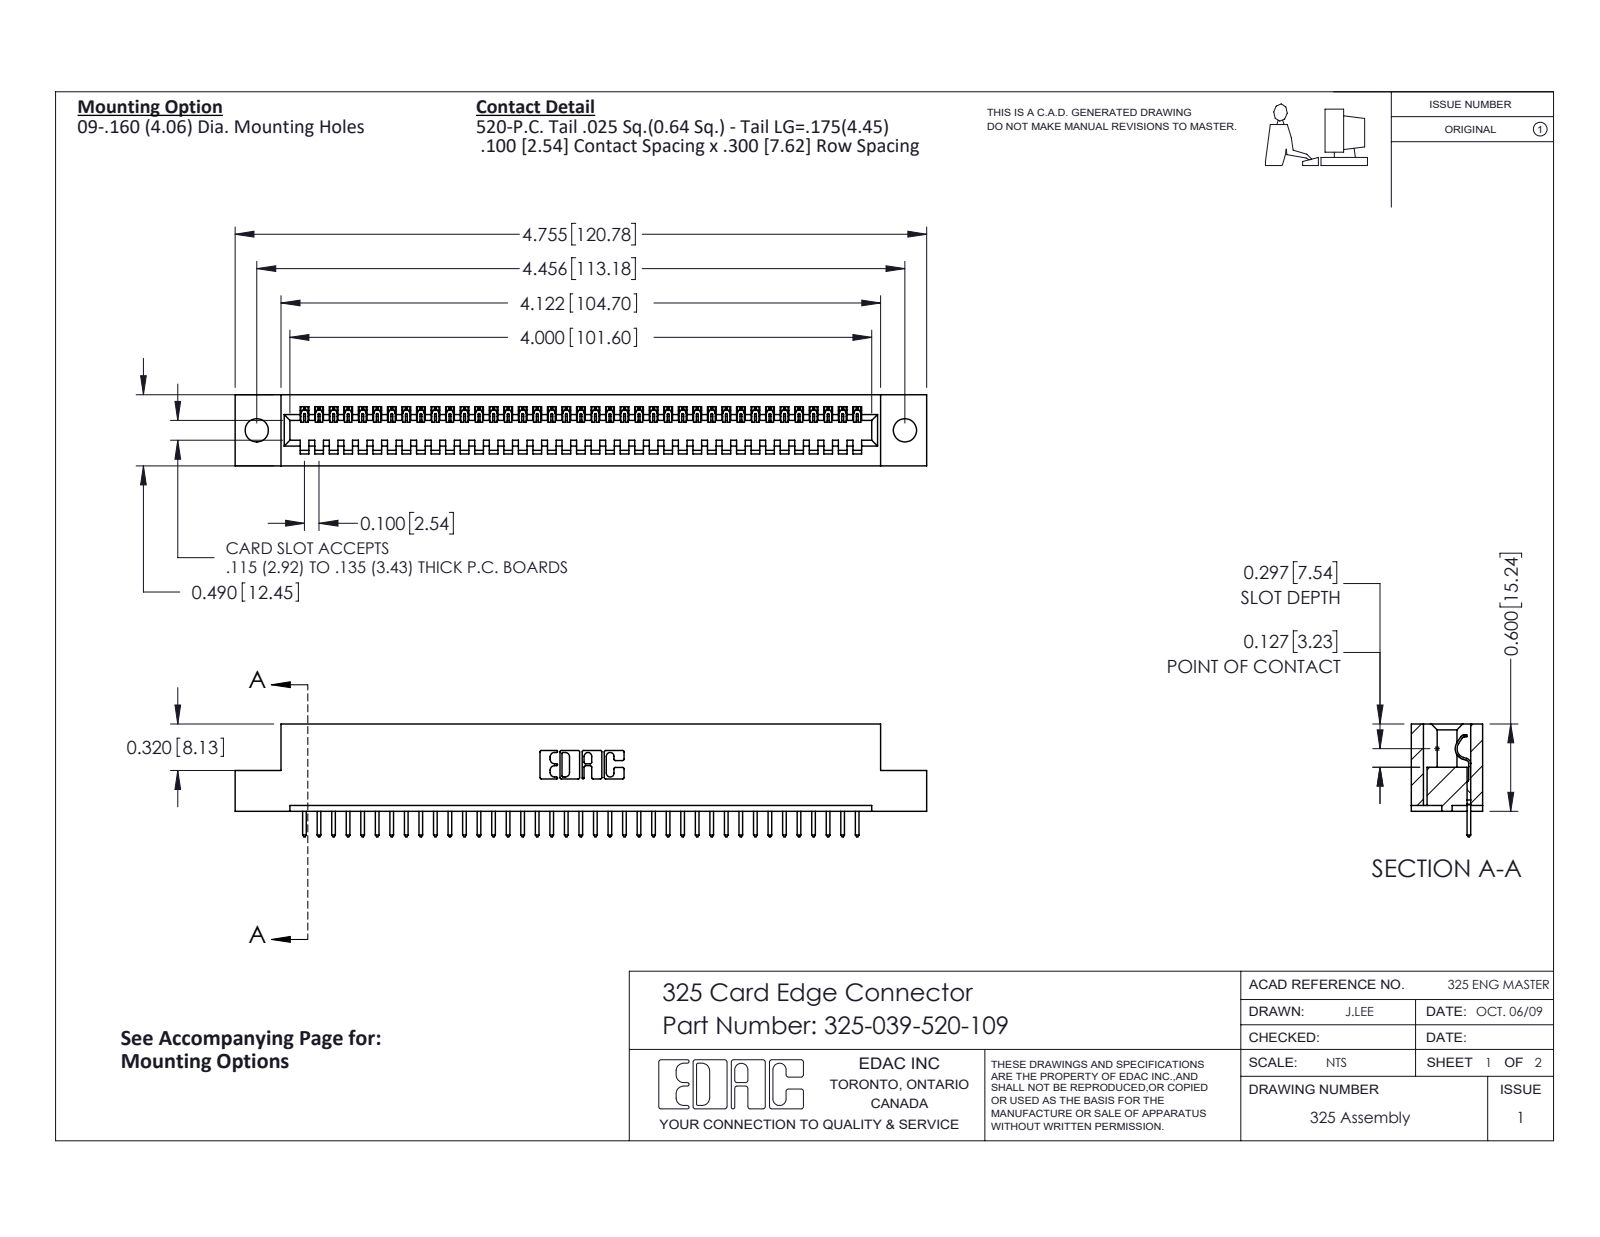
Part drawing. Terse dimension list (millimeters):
name: 325-292-001_325-293-120; 325-039-520-109; 325 Part_.160 TH
written by: SolidWorks 2016 (CONFIG_CONTROL_DESIGN)
unit: mm
bodies: 40 solids, 2376 faces (1708 planar, 668 cylindrical, 0 other)
size: 120.8 × 19.7 × 12.4
volume: 15 000 mm³; area: 15 800 mm²
holes: 2× ⌀4.1
rounds: 78× R0.2, 78× R0.3, 22× R0.3, 6× R0.2, 6× R0.8, 3× R0.7, 1× R0.4, 1× R0.6
face distances: 2.1, 10.3, 12.4, 7.6, 2.7, 9.7, 0.6, 8.3, 14.2, 1
hole spacings: 113.2
